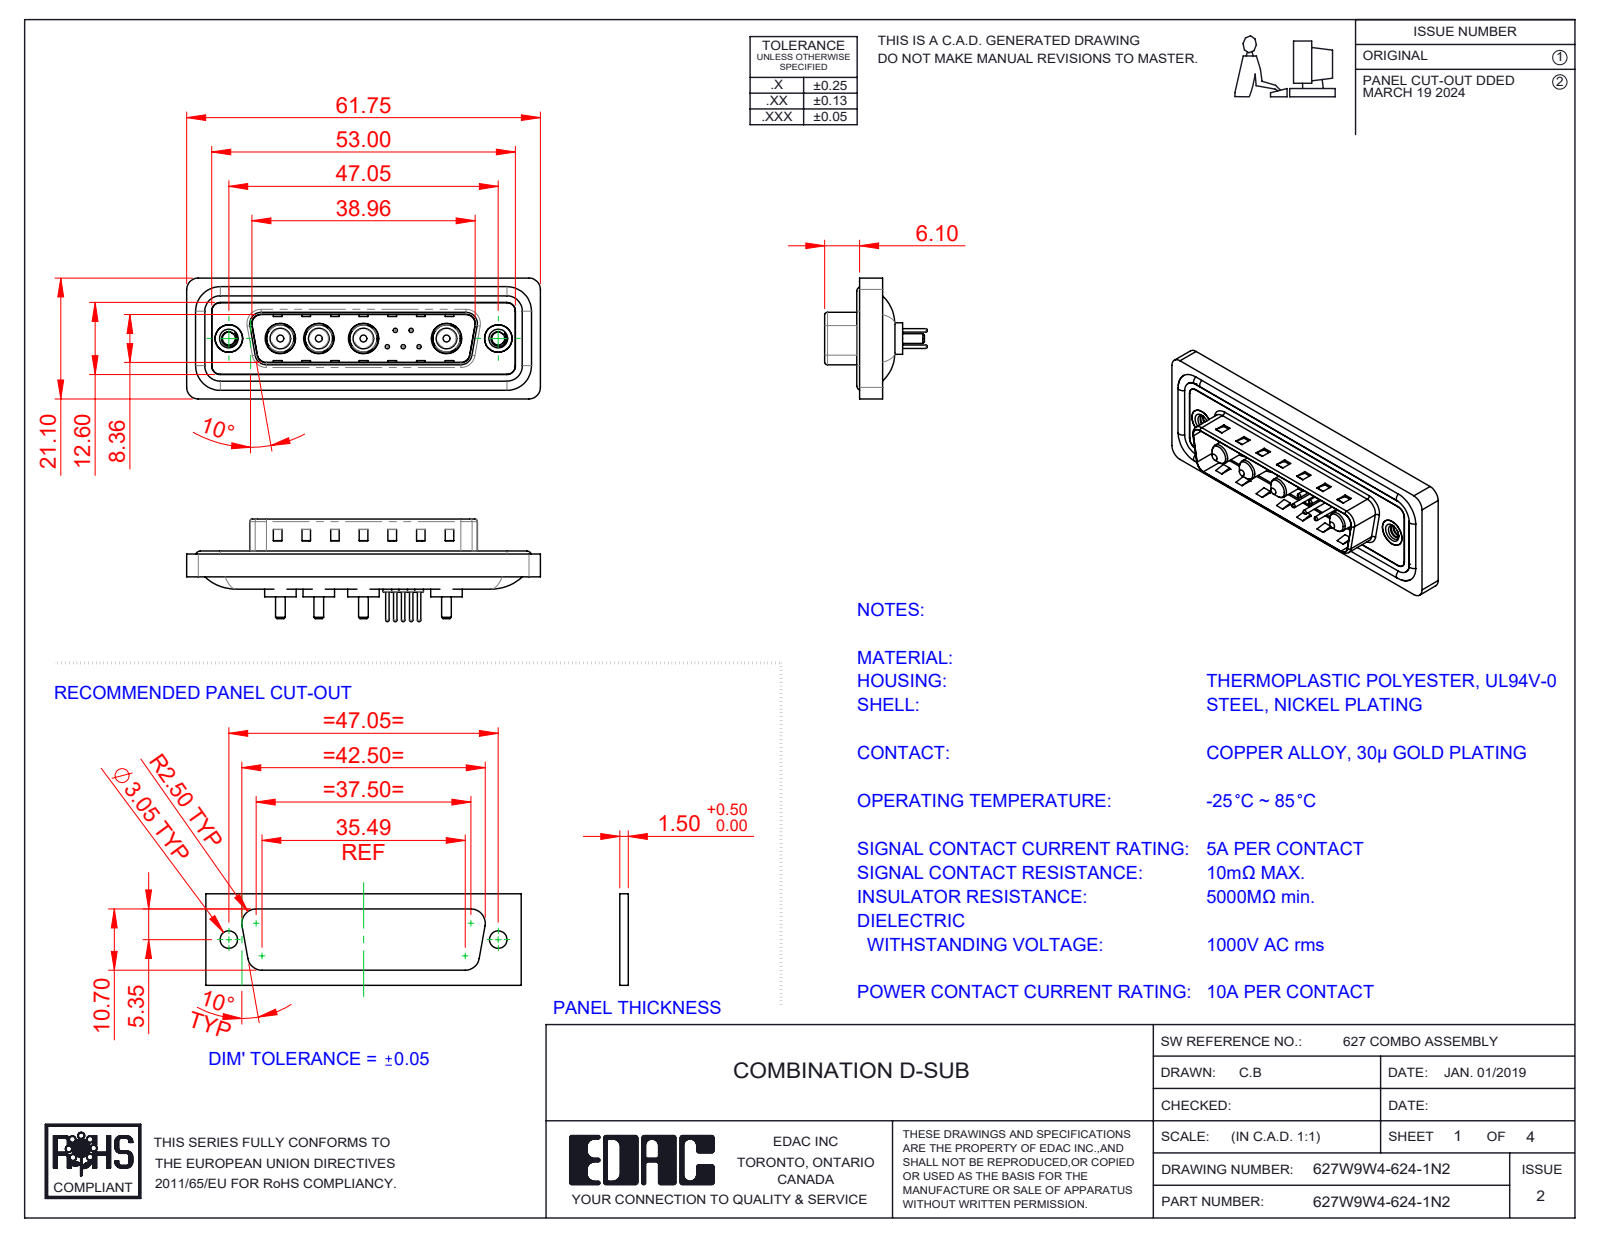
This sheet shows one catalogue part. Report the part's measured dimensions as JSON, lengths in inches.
{"part_name": "627W9W4-624-1N2; Power Pin_10A S; 627Combo Housing_9W4; 627Combo Shell Rear_25 Contacts (+5 more)", "step_written_by": "SolidWorks 2023 (CONFIG_CONTROL_DESIGN)", "units": "inches", "bodies": {"solids": 20, "faces": 824, "planar": 284, "cylindrical": 334, "other": 206}, "overall_size": [2.431, 0.831, 0.705], "volume_in3": 0.448, "surface_area_in2": 18.27, "round_holes": [[0.03, 5], [0.063, 5], [0.079, 5], [0.191, 4], [0.209, 4], [0.089, 2], [0.157, 2], [0.189, 2], [0.197, 2]], "round_bosses_or_shafts": [[0.059, 5], [0.024, 5], [0.217, 4], [0.205, 4], [0.187, 4], [0.148, 4], [0.142, 4], [0.067, 4]], "partial_cylinders_radius": [[0.059, 22], [0.079, 18], [0.02, 8], [0.063, 8], [0.01, 4], [0.024, 4], [0.026, 4], [0.035, 4]], "face_to_face_distances": [0.016, 0.059, 0.043, 0.02, 0.122, 0.063, 0.114, 0.032, 0.377, 0.222], "hole_center_spacings": [0.124, 0.109, 0.198, 0.571, 0.109, 0.173, 0.174, 0.197]}
